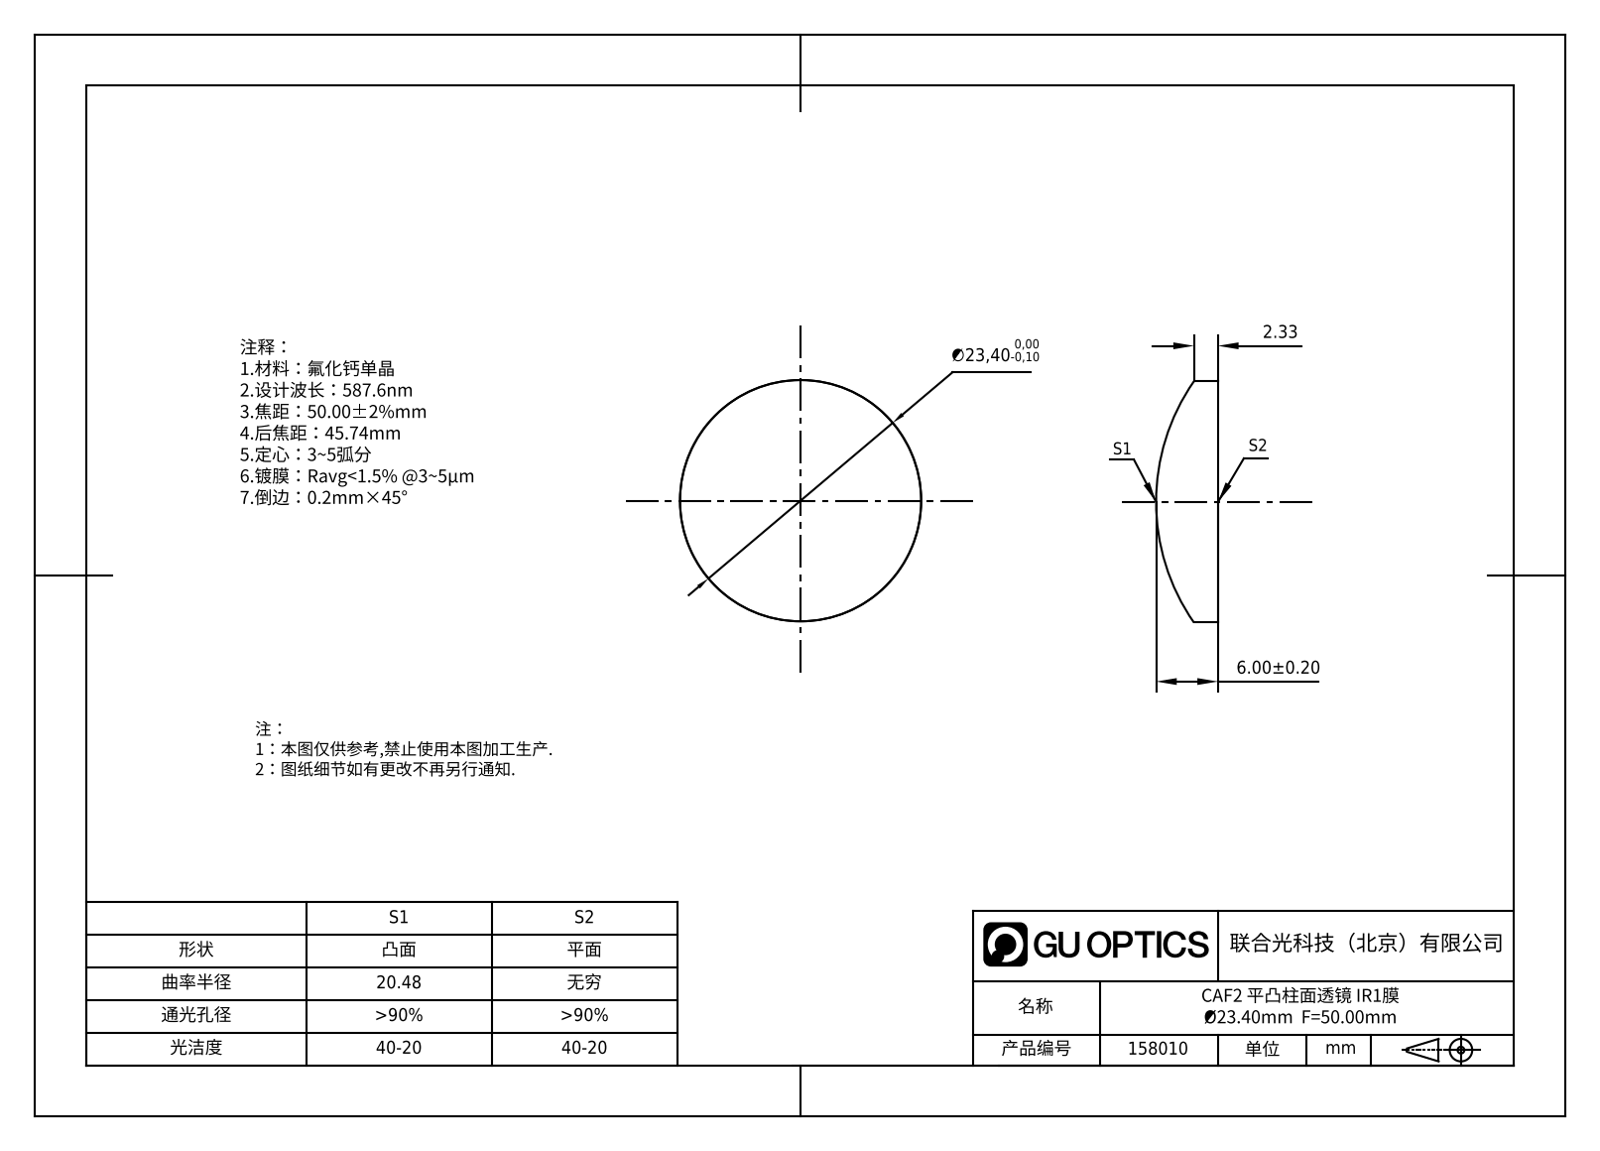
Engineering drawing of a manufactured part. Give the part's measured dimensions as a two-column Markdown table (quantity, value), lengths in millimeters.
| quantity | value |
| --- | --- |
| part name | GL55-025-050-IR1 |
| STEP written by | SolidWorks 2022 (AUTOMOTIVE_DESIGN) |
| units | millimeters |
| bodies | 1 solid, 9 faces (1 planar, 4 cylindrical, 4 other) |
| overall size | 23.4 × 23.4 × 6 |
| volume | 2 199 mm³ |
| surface area | 1 175 mm² |
| round bosses / shafts (diameter × count) | 23.4 × 1 |
| partial cylindrical surfaces (radius × count) | 20.48 × 1 |
